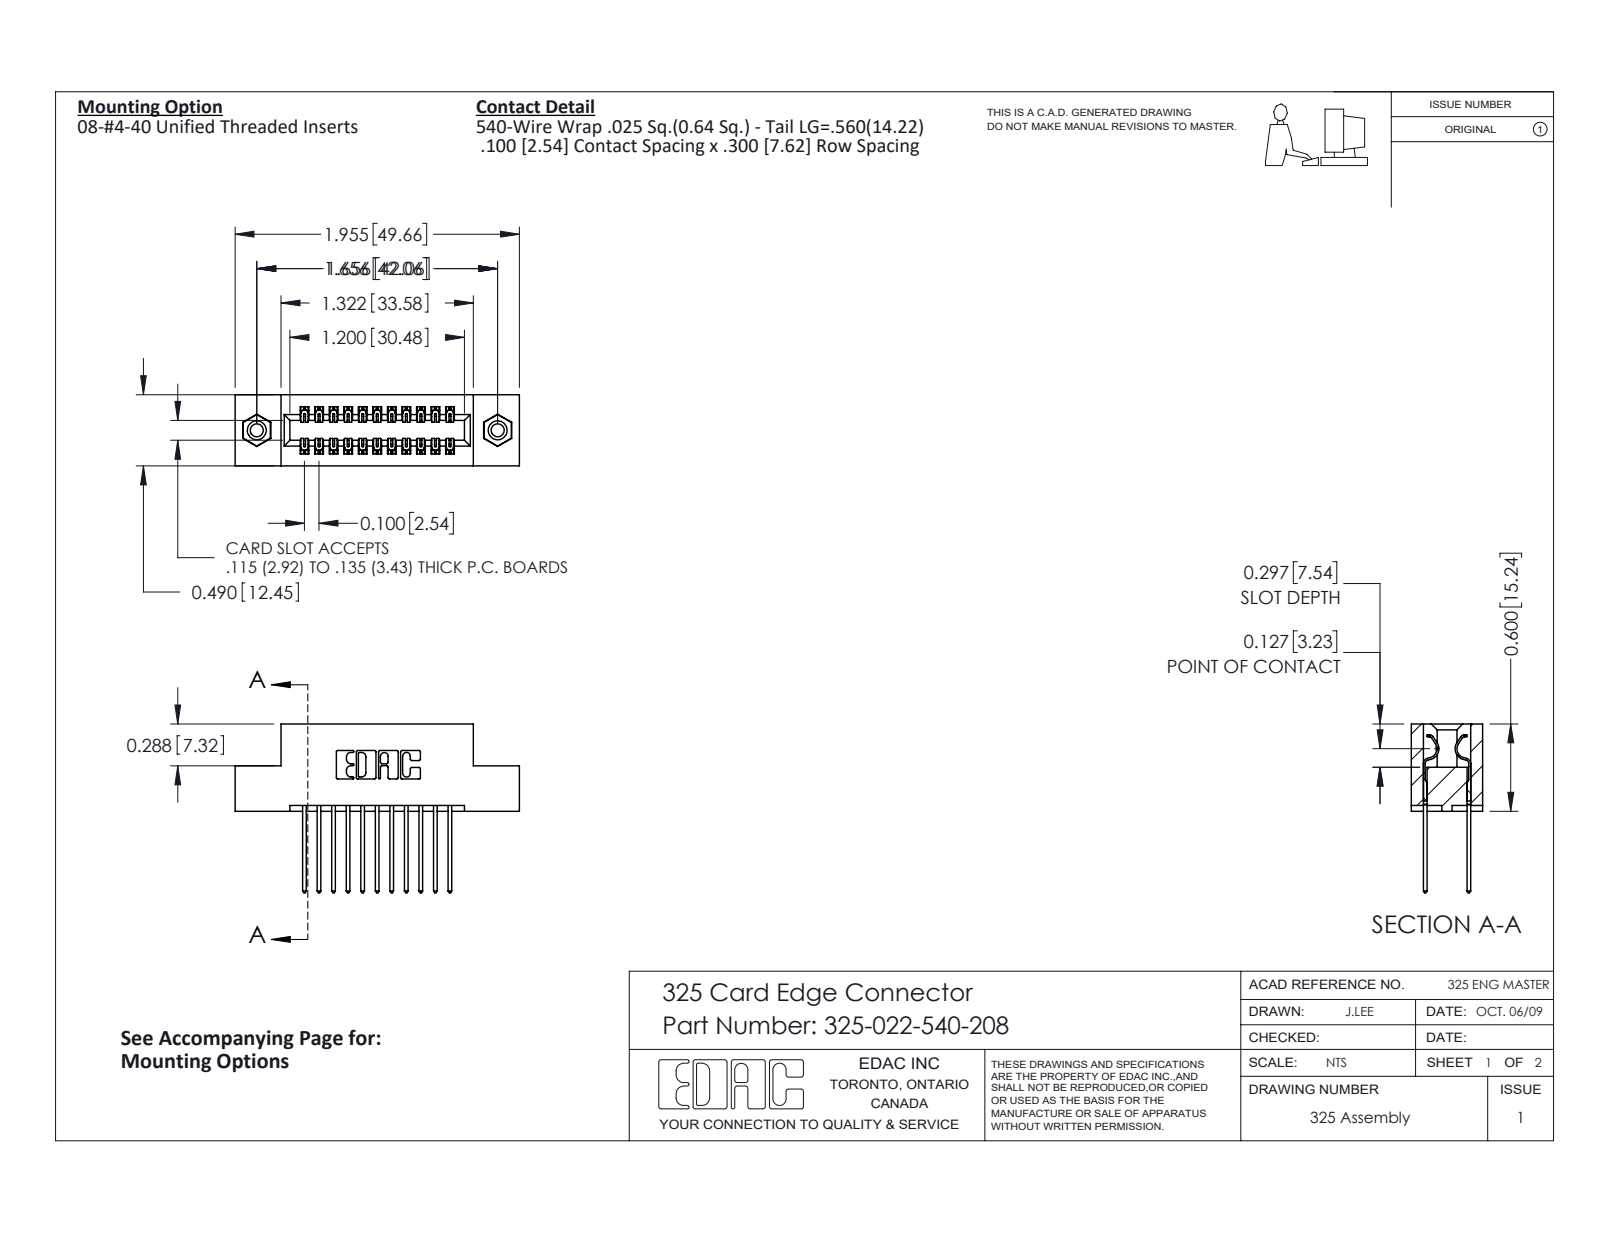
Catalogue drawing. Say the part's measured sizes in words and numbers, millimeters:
The part is named "325-292-001_325-293-140; 325 Part_TI; 325-022-540-208; 345-250-001_345-250-003-102". Its 3-D file was written by "SolidWorks 2016 (CONFIG_CONTROL_DESIGN)". It is 25 solids with 1318 faces: 894 planar, 408 cylindrical and 16 other. Overall it measures 49.7 by 29.5 by 12.4 millimeters. Its volume is 6 210 cubic millimeters and its surface area 7 194 square millimeters. Round holes: 2 of diameter 2.3, 2 of diameter 3.2, 2 of diameter 4.1. Round bosses or shafts: 2 of diameter 3.9. Partial cylindrical surfaces (rounded edges, fillets, slot ends): 33 of radius 0.2, 22 of radius 0.3, 22 of radius 0.3, 6 of radius 0.2, 6 of radius 0.8, 3 of radius 0.7, 2 of radius 0.4, 2 of radius 0.6. The main face-to-face distances are 7.6, 2.1, 10.3, 12.4, 2.7, 9.7, 0.6, 1, 2.5, 5.1. The hole center spacings are 42.1.
